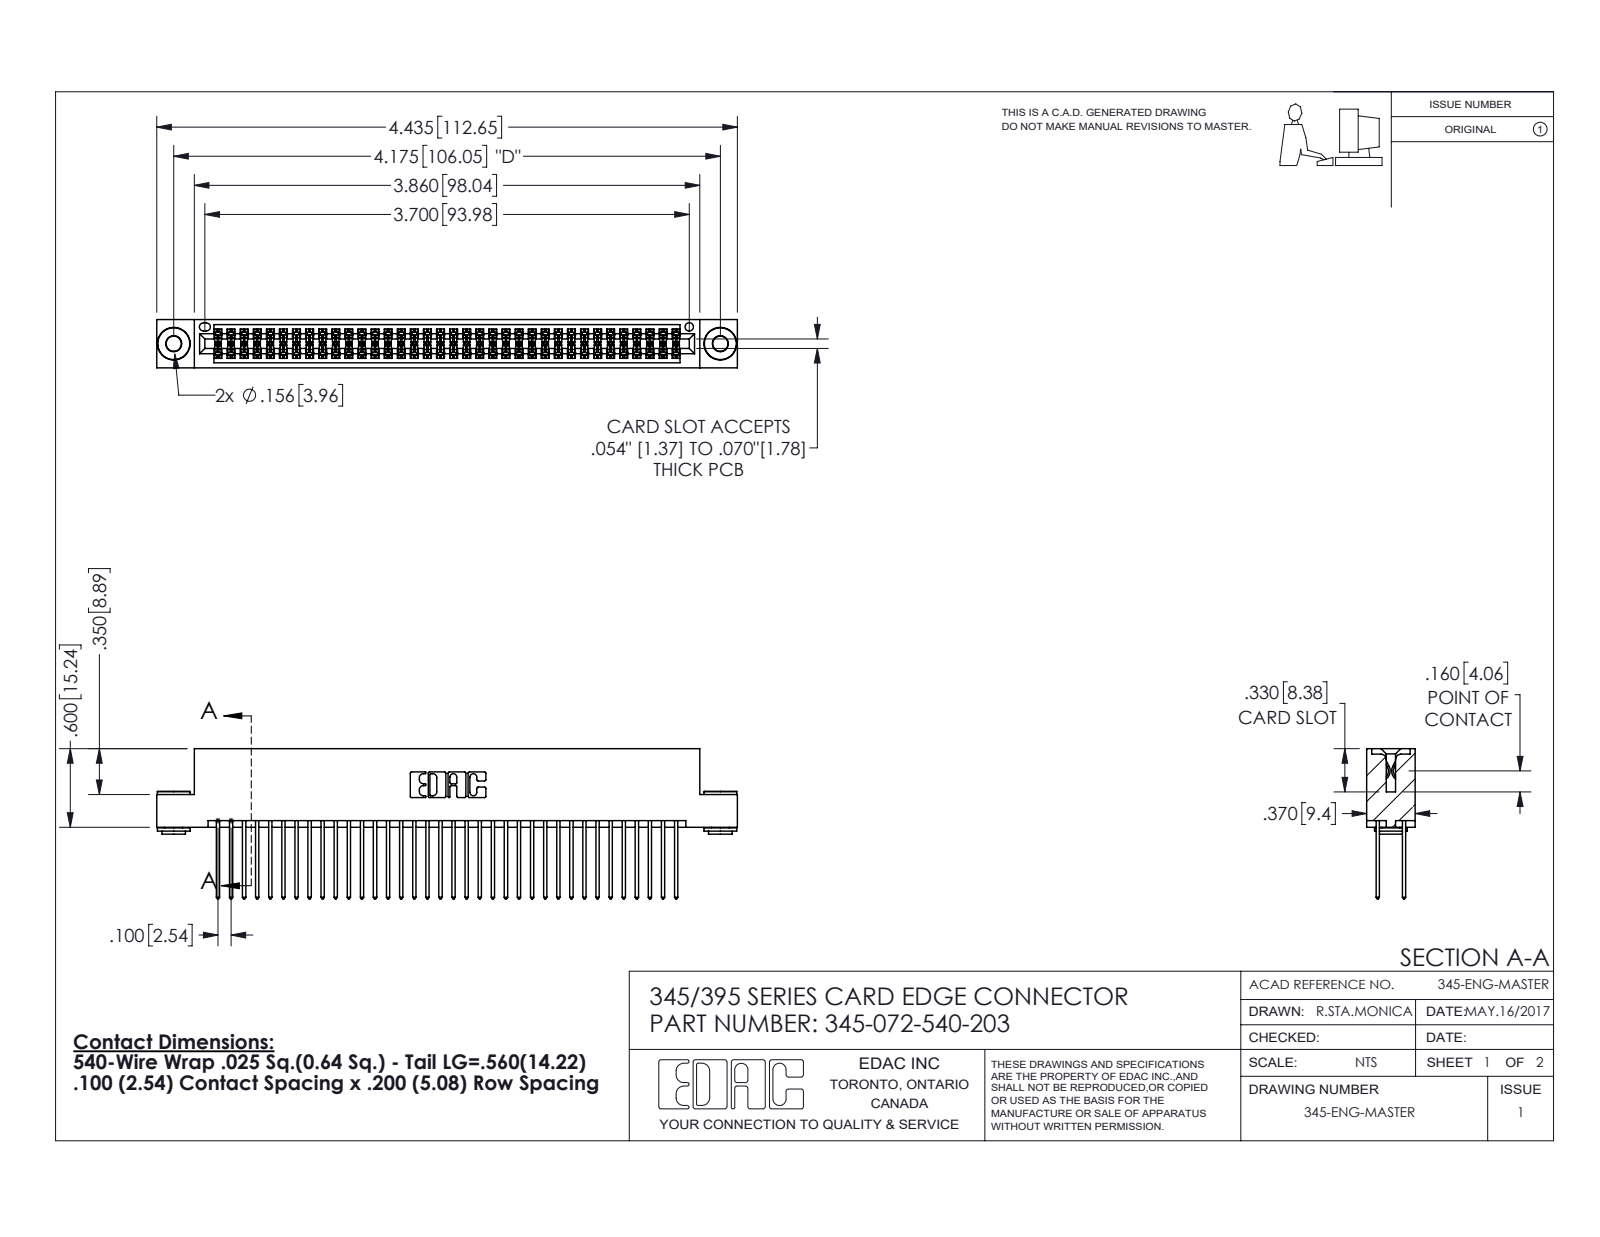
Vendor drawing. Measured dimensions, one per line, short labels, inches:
name: 345-292-001_345-293-140; 345 Part_Flush Mounting Lugs - 0.156 Dia-TH; 345-072-540-203; 345-250-002_345-250-002-102
written by: SolidWorks 2016 (CONFIG_CONTROL_DESIGN)
unit: in
bodies: 75 solids, 3764 faces (2466 planar, 1290 cylindrical, 8 other)
size: 4.435 × 1.147 × 0.37
volume: 0.682 in³; area: 27.71 in²
holes: 2× ⌀0.116, 2× ⌀0.156, 1× ⌀0.064
bosses: 2× ⌀0.25, 2× ⌀0.18, 2× ⌀0.136
rounds: 108× R0.006, 72× R0.01, 22× R0.01, 6× R0.007, 6× R0.031, 3× R0.026, 2× R0.014, 2× R0.019
face distances: 0.072, 0.298, 0.2, 0.025, 0.098, 0.272, 0.37, 0.225, 0.175, 0.149
hole spacings: 0.27, 3.939, 4.175
